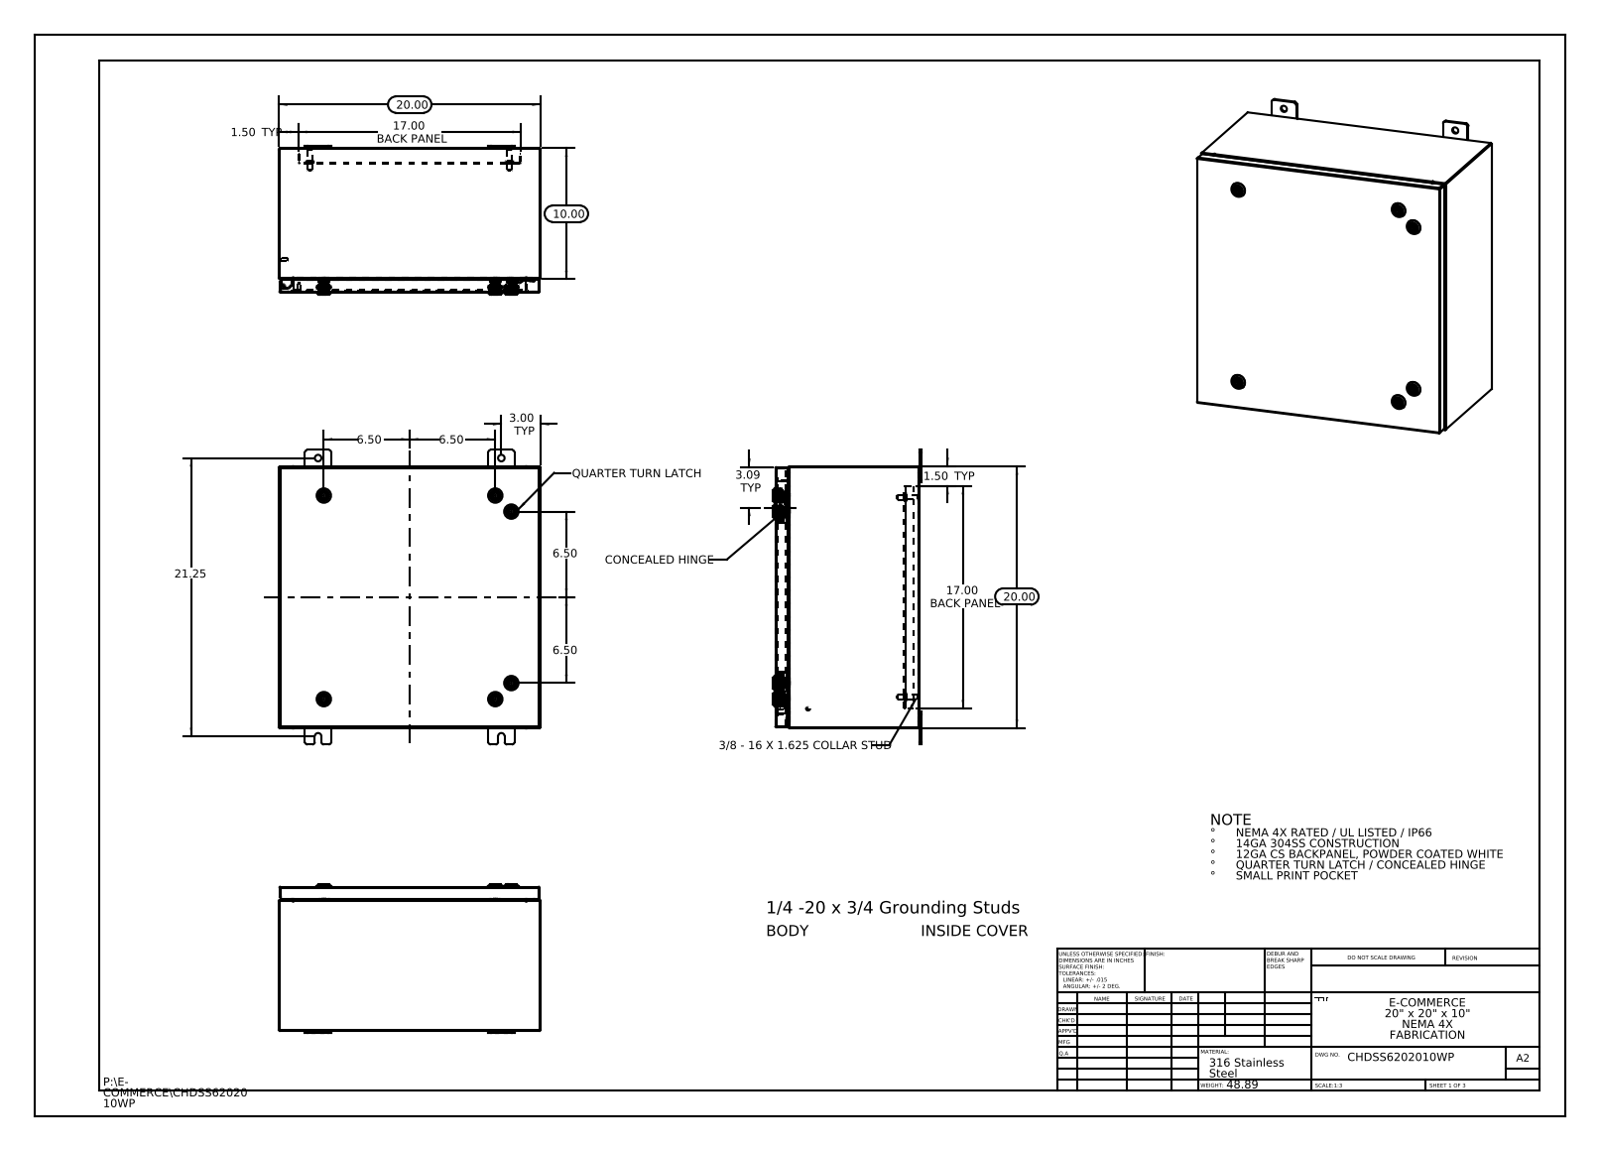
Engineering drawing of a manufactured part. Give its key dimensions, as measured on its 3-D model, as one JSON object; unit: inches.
{"part_name": "Concealed Hinge (Cover Side); HW-CLH-E5-8004_Cam-232112-U-Industrilas; CHDSS6202010WP Body; CHDSS6202010WP Cover (+8 more)", "step_written_by": "SolidWorks 2013 (CONFIG_CONTROL_DESIGN)", "units": "inches", "bodies": {"solids": 55, "faces": 5420, "planar": 1592, "cylindrical": 1692, "other": 2136}, "overall_size": [22.5, 20, 11.356], "volume_in3": 175.1, "surface_area_in2": 4406, "round_holes": [[0.5, 8], [0.197, 6], [0.394, 6], [0.4, 6], [0.63, 6], [0.787, 6], [0.136, 4], [0.211, 1]], "round_bosses_or_shafts": [[0.236, 8], [1.102, 6], [0.78, 6], [0.626, 6], [0.61, 6], [0.531, 6], [0.392, 6], [0.114, 6]], "partial_cylinders_radius": [[0.006, 198], [0.118, 198], [0.028, 72], [0.02, 24], [0.19, 24], [0.197, 24], [0.013, 20], [0.088, 18]], "face_to_face_distances": [0.075, 19.925, 0.074, 19.85, 20, 11.01, 10.935, 10.936, 10.861, 0.104], "hole_center_spacings": [13.1, 14.378, 1.858, 3.065, 14, 14.164, 14.187, 15.25]}
